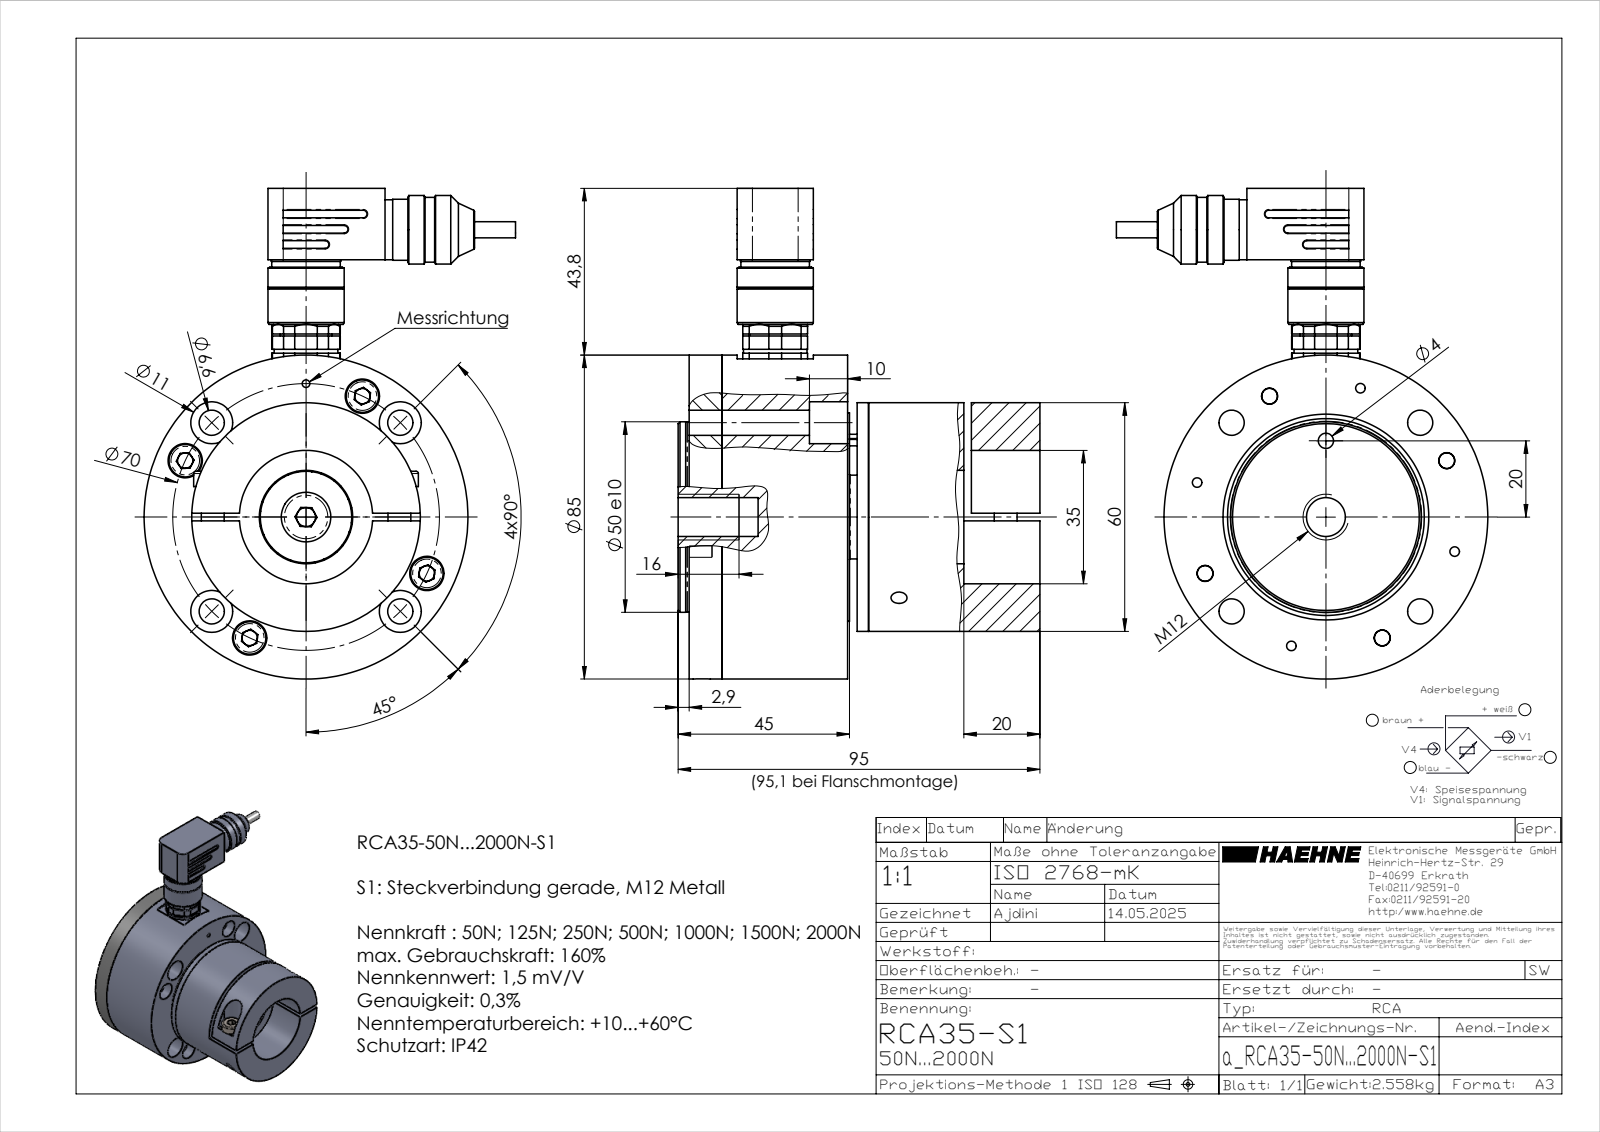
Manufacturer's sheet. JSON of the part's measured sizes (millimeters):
{"part_name": "inafag_1203-tvh_7zkvytp7yxkimpdvw8sj0b5w4_23; inafag_1203-tvh_7zkvytp7yxkimpdvw8sj0b5w4_15; inafag_1203-tvh_7zkvytp7yxkimpdvw8sj0b5w4_02; inafag_1203-tvh_7zkvytp7yxkimpdvw8sj0b5w4_22 (+8 more)", "step_written_by": "SolidWorks 2023 (AUTOMOTIVE_DESIGN)", "units": "millimeters", "bodies": {"solids": 55, "faces": 808, "planar": 408, "cylindrical": 228, "other": 172}, "overall_size": [128.75, 97.48, 95.1], "volume_mm3": 372197, "surface_area_mm2": 116244, "round_holes": [[3.4, 9], [2.5, 8], [6.6, 6], [4.2, 5], [4, 4], [5.3, 4], [9, 4], [11, 4], [4.5, 2], [5, 2], [2, 1], [6, 1]], "round_bosses_or_shafts": [[3, 9], [5.7, 8], [8.5, 4], [5, 4], [1.5, 4], [1, 4], [18, 2], [17, 2]], "partial_cylinders_radius": [[0.2, 12], [1, 11], [0.3, 6], [4, 2], [5.5, 2], [0.57, 1], [0.65, 1], [0.77, 1]], "face_to_face_distances": [3, 2, 8.6, 47.1, 35.5, 11.6, 45, 30, 50, 50.1], "hole_center_spacings": [35, 49.5, 24.78, 25.2, 32.8, 51.14, 56.46, 6]}
